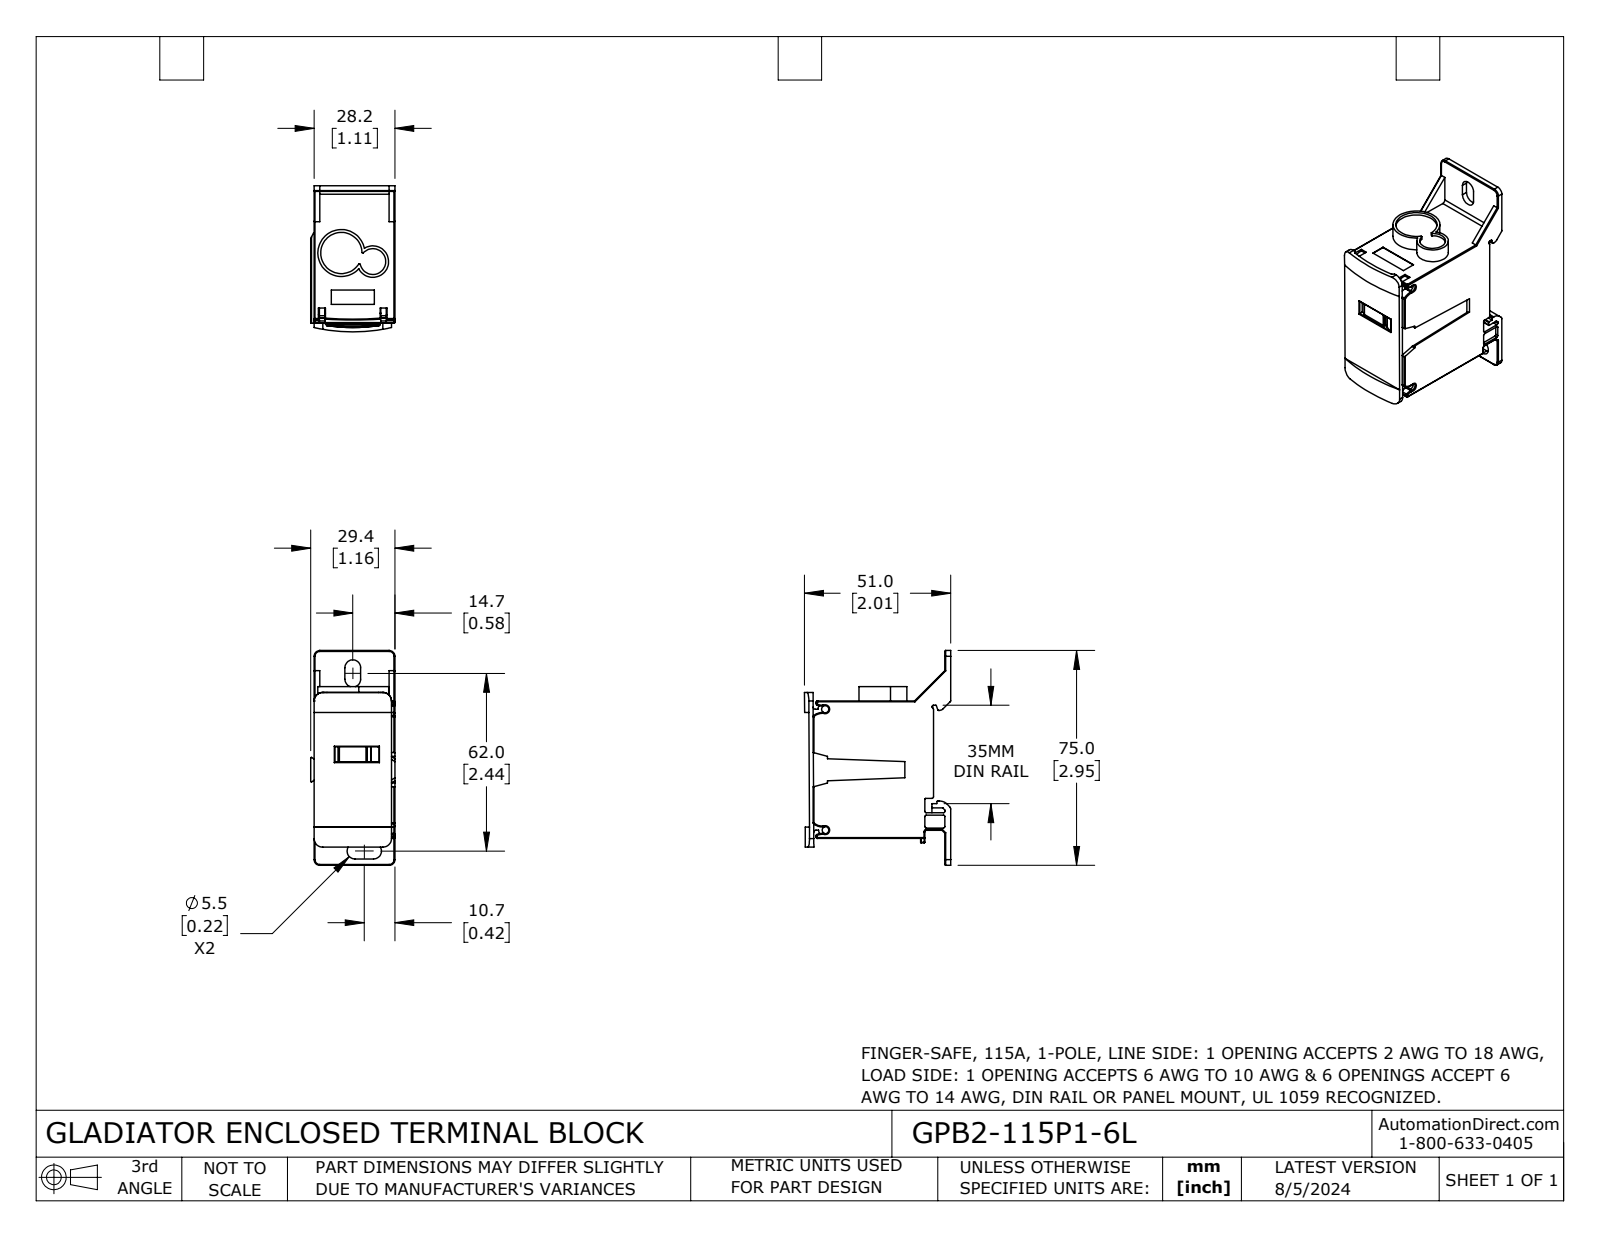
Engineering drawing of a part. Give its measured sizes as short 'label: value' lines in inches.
name: GPB2-115P1-6L
written by: SolidWorks 2023 (CONFIG_CONTROL_DESIGN)
unit: in
bodies: 1 solid, 469 faces (171 planar, 228 cylindrical, 70 other)
size: 2.953 × 2.009 × 1.157
volume: 3.751 in³; area: 23.02 in²
holes: 1× ⌀0.098, 1× ⌀0.354, 1× ⌀0.567
bosses: 1× ⌀0.646, 1× ⌀0.098
rounds: 61× R0.008, 29× R0.012, 20× R0.02, 7× R0.197, 5× R0.079, 4× R0.108, 4× R0.118, 3× R0.207
face distances: 1.11, 0.079, 0.157, 0.236, 0.039, 1.89, 1.85, 0.059, 0.276, 2.047
hole spacings: 0.449
